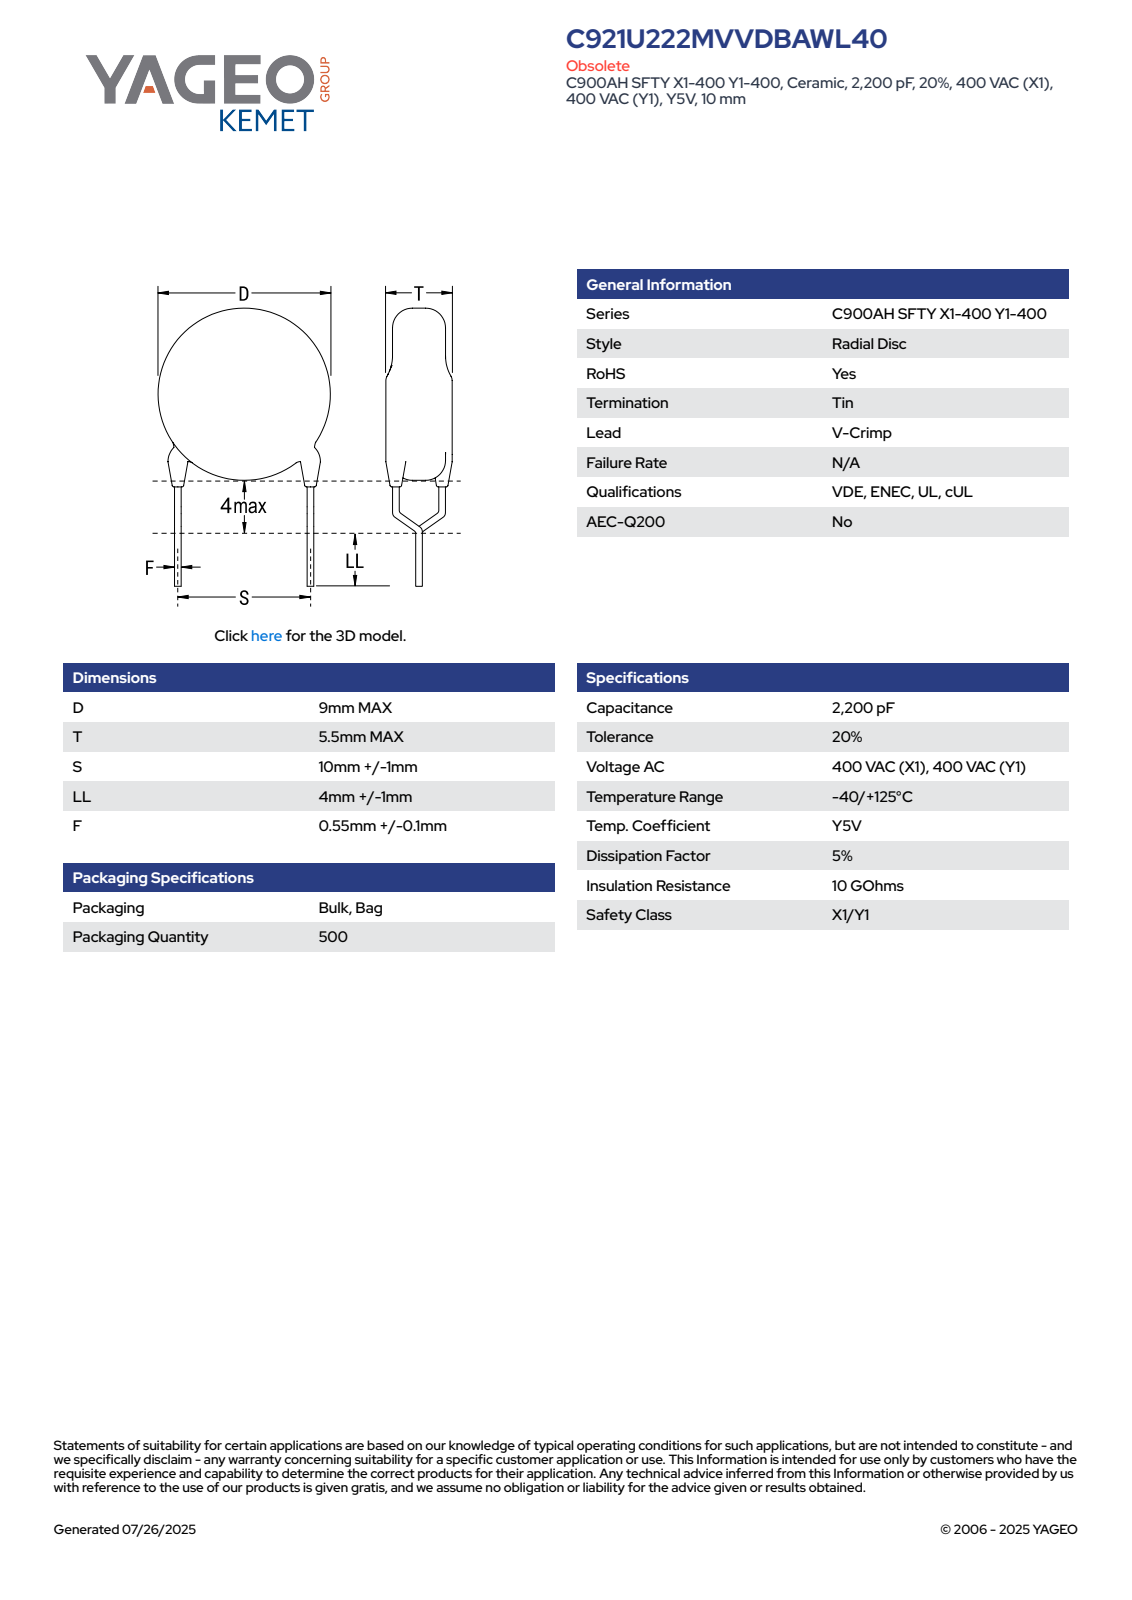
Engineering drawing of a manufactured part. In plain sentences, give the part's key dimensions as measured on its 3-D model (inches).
The part is named "CCD_VCC900_D9T5.5S10LL5F0.65". Its 3-D file was written by "SolidWorks 2014 (AUTOMOTIVE_DESIGN)". It is 5 solids with 93 faces: 65 planar, 16 cylindrical and 12 other. Overall it measures 0.701 by 0.419 by 0.217 inches. Its volume is 0.021 cubic inches and its surface area 0.493 square inches. Round bosses or shafts: 6 of diameter 0.026, 1 of diameter 0.354. The main face-to-face distances are 0.217, 0.311, 0.046, 0.546, 0.235, 0.5, 0.189, 0.013, 0.188, 0.137.
